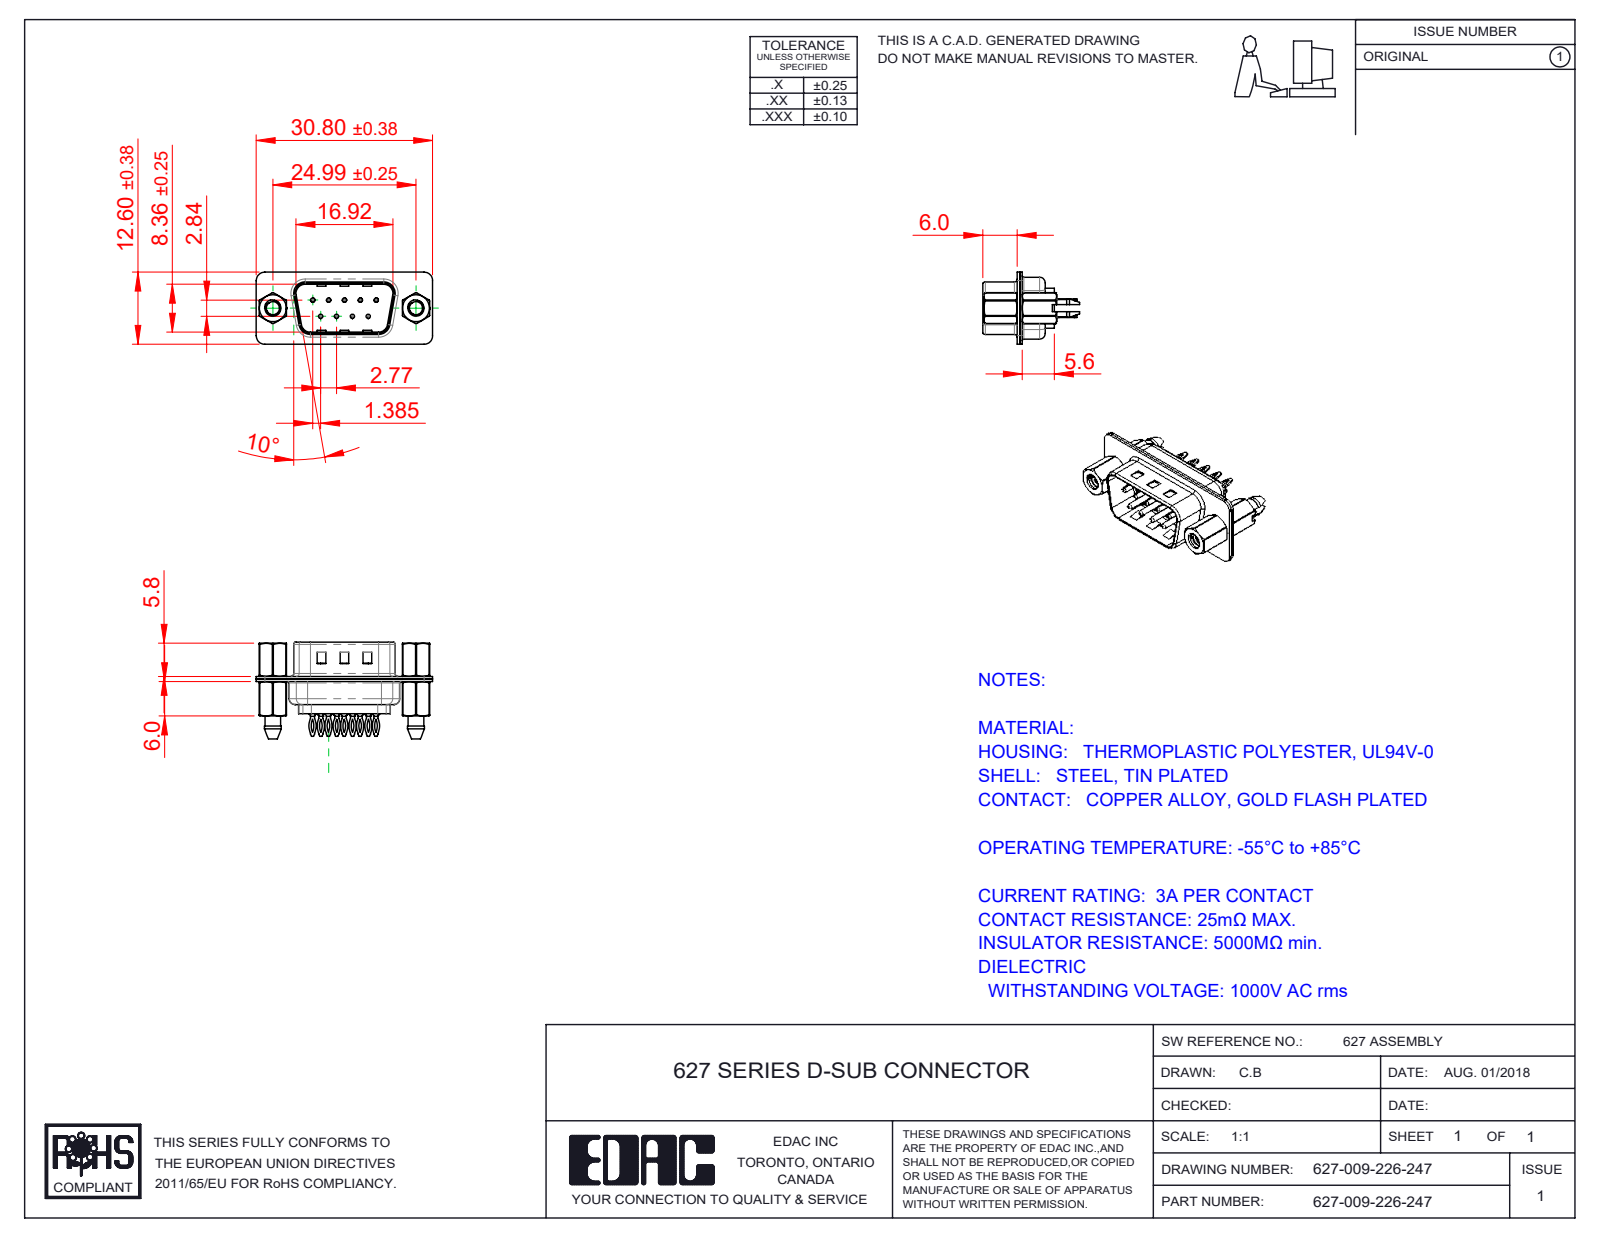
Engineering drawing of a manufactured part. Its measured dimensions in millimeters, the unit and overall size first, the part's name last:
Units: millimetres
Overall size (bounding box): 30.8 × 16.9 × 12.6
Round holes (diameter × count): ⌀0.35 ×9, ⌀1.1 ×9, ⌀1.6 ×9, ⌀2.26 ×2, ⌀2.29 ×2, ⌀4 ×2, ⌀4.8 ×2
Round bosses / shafts (diameter × count): ⌀2 ×9, ⌀1.5 ×9, ⌀0.75 ×9, ⌀4.9 ×2, ⌀2.79 ×2
Partial cylindrical surfaces — rounded edges, fillets, slot ends (radius × count): R1.5 ×20, R2.92 ×18, R3.33 ×18, R2 ×12, R1.6 ×10, R0.5 ×8, R0.25 ×4, R0.6 ×4
Main face-to-face distances: 0.45, 0.4, 0.9, 0.82, 9.58, 1.4, 4.76, 8.76, 6.5, 0.5
Hole centre spacings: 3.16, 2.77, 5.54, 5.03, 5.04, 8.31, 7.48, 7.49
Volume: 1 639 mm³ · Surface area: 4 680 mm²
Bodies: 16 solids, 1188 faces (341 planar, 512 cylindrical, 335 other)
Part name (STEP PRODUCT): 627 Shell Rear_09 Contacts; 627 4-40 Threaded Boardlock_LP; 627 4-40 Hex Standoff; 627 Contact Row 1_26L (+4 more)
STEP written by: SolidWorks 2020 (CONFIG_CONTROL_DESIGN)
